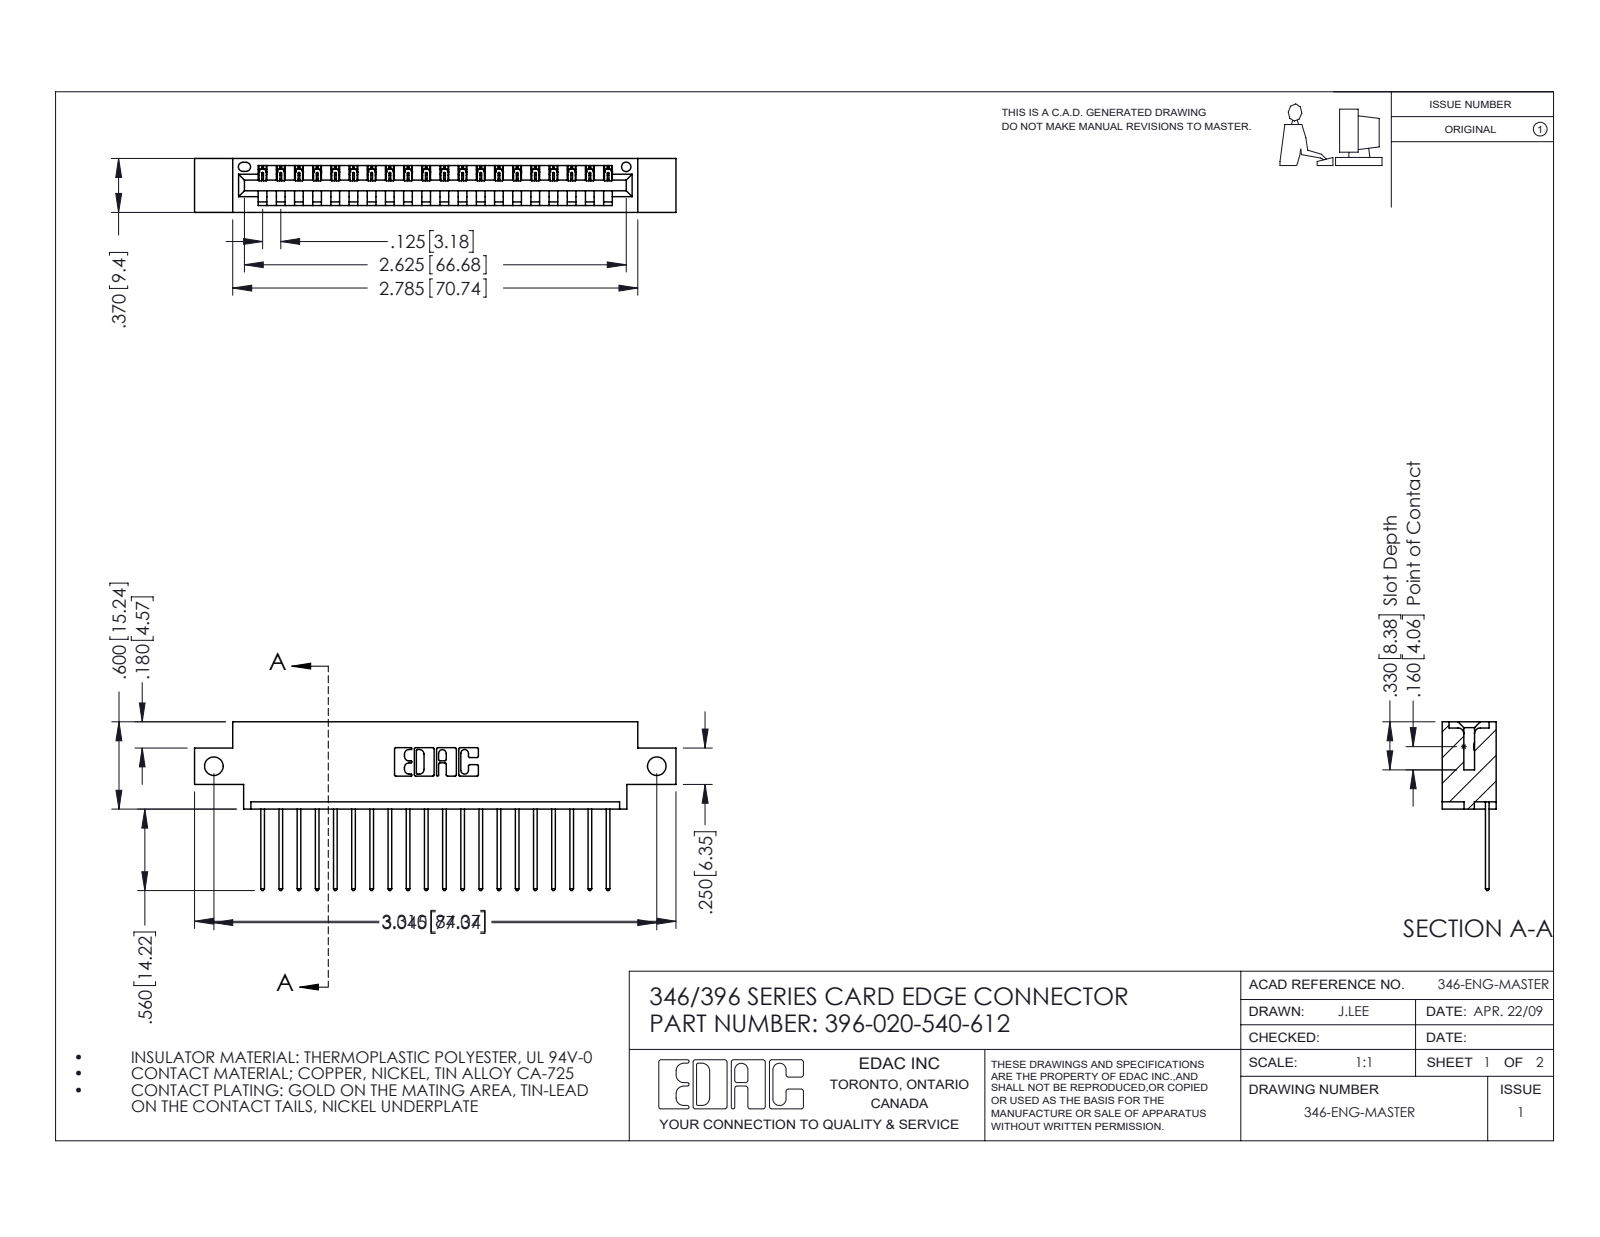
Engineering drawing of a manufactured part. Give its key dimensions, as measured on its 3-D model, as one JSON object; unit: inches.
{"part_name": "396-020-540-612; 345-292-001_345-293-140; 346 Part_0.170 Offset - Side Mount", "step_written_by": "SolidWorks 2016 (CONFIG_CONTROL_DESIGN)", "units": "inches", "bodies": {"solids": 21, "faces": 1286, "planar": 880, "cylindrical": 406, "other": 0}, "overall_size": [3.31, 1.16, 0.37], "volume_in3": 0.469, "surface_area_in2": 14.84, "round_holes": [[0.128, 2], [0.064, 1]], "partial_cylinders_radius": [[0.006, 40], [0.01, 40], [0.01, 22], [0.007, 6], [0.031, 6], [0.026, 3], [0.031, 2], [0.04, 2]], "face_to_face_distances": [0.048, 0.322, 0.37, 0.25, 0.072, 0.298, 0.025, 0.148, 0.222, 0.1], "hole_center_spacings": [3.045]}
